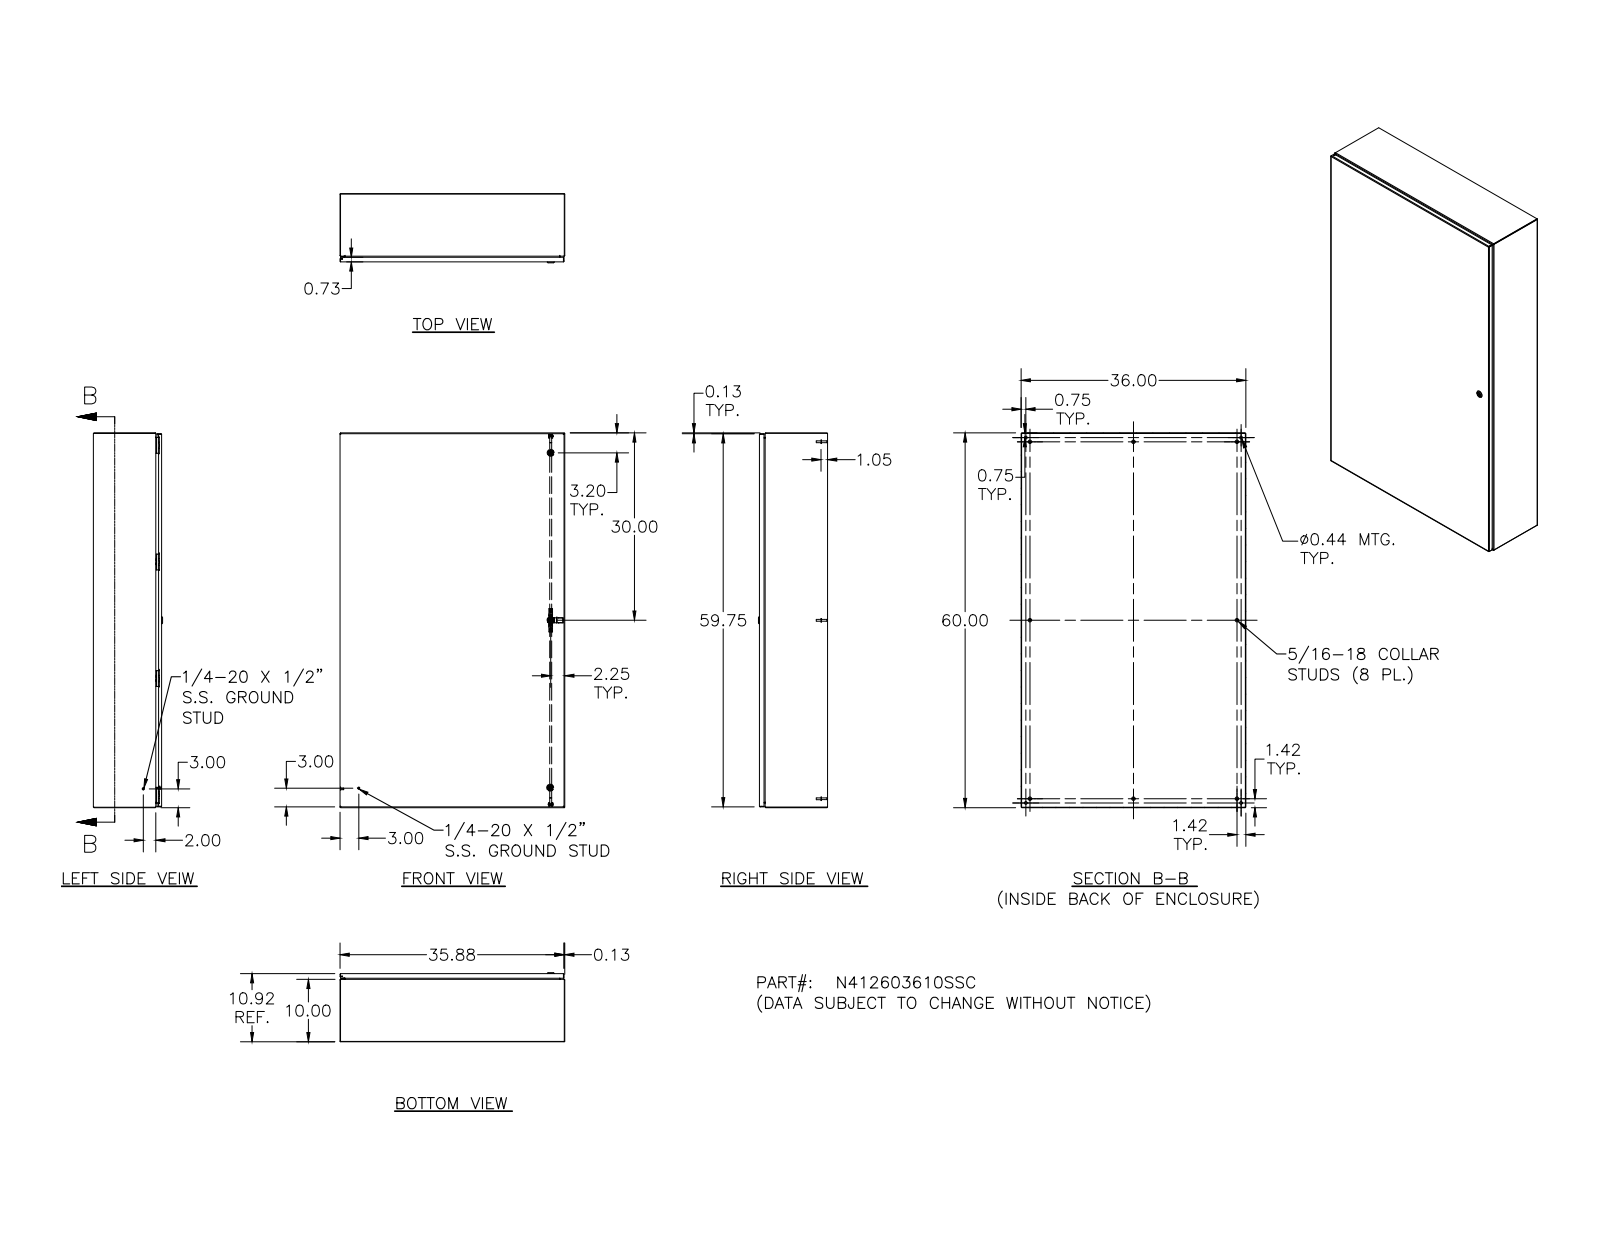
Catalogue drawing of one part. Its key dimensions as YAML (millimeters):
part_name: "N412603610SSC; N412603610SSCBLR; N4123610SSCTB; 388151 (+8 more)"
step_written_by: "Autodesk Inventor 2011 (AUTOMOTIVE_DESIGN)"
units: millimeters
bodies: {solids: 81, faces: 2661, planar: 988, cylindrical: 992, other: 681}
overall_size: [1524, 914.4, 281.3]
volume: 8128000
surface_area: 8631000
round_holes:
  - {diameter: 2.4, count: 8}
  - {diameter: 3.9, count: 8}
  - {diameter: 4.2, count: 8}
  - {diameter: 4.4, count: 8}
  - {diameter: 4.7, count: 8}
  - {diameter: 5, count: 5}
  - {diameter: 4, count: 4}
  - {diameter: 4.2, count: 4}
  - {diameter: 11.1, count: 4}
  - {diameter: 2.7, count: 2}
  - {diameter: 4.1, count: 2}
  - {diameter: 4.3, count: 2}
round_bosses_or_shafts:
  - {diameter: 6.4, count: 18}
  - {diameter: 14.3, count: 8}
  - {diameter: 9.1, count: 8}
  - {diameter: 8.1, count: 8}
  - {diameter: 7.6, count: 8}
  - {diameter: 7, count: 8}
  - {diameter: 6.5, count: 8}
  - {diameter: 4.2, count: 8}
partial_cylinders:
  - {radius: 1.3, count: 50}
  - {radius: 0.8, count: 36}
  - {radius: 0.4, count: 34}
  - {radius: 3.2, count: 32}
  - {radius: 0.3, count: 30}
  - {radius: 0.5, count: 20}
  - {radius: 2.7, count: 18}
  - {radius: 3, count: 18}
face_to_face_distances: [1.9, 275.4, 273.5, 277.3, 912.5, 1522.1, 910.6, 914.4, 1520.2, 1524]
hole_center_spacings: [474.1, 948.3, 474.1, 1422.4, 12.7, 16.7, 33.2, 474.3]
